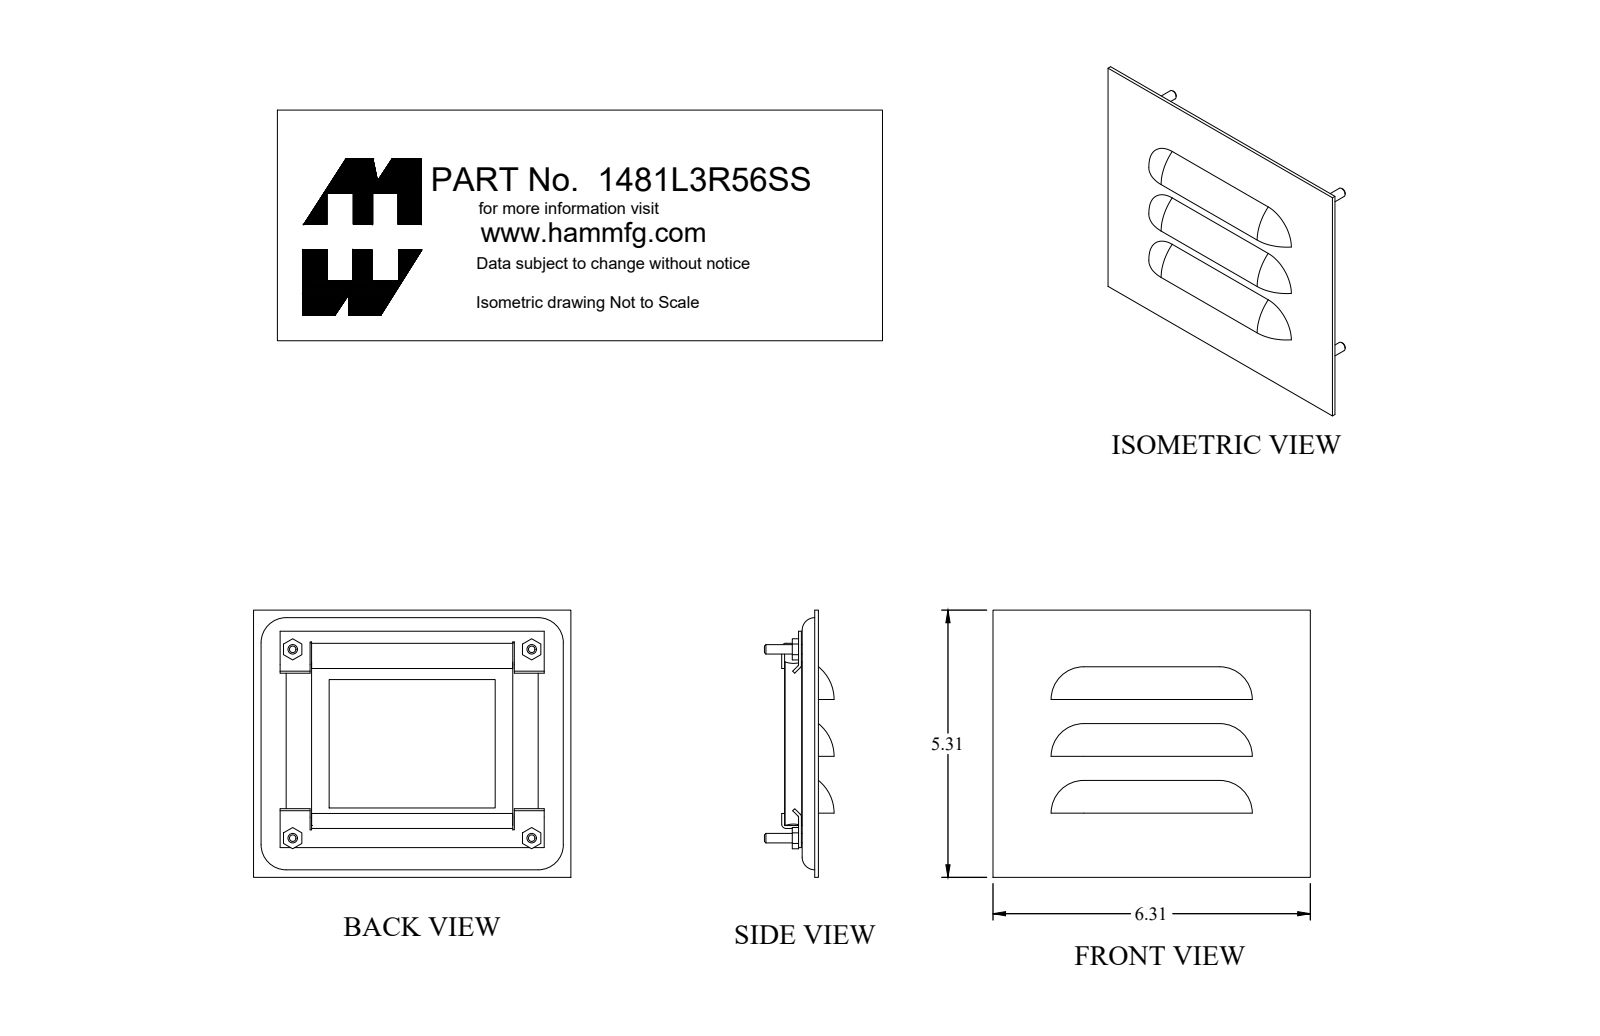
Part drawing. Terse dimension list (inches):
name: 1481L3R56SS_Default
written by: SolidWorks 2019 (CONFIG_CONTROL_DESIGN)
unit: in
bodies: 13 solids, 240 faces (138 planar, 70 cylindrical, 32 other)
size: 6.308 × 5.308 × 1.041
volume: 8.702 in³; area: 175 in²
holes: 4× ⌀0.156, 4× ⌀0.205
bosses: 4× ⌀0.25, 4× ⌀0.188
rounds: 6× R0.029, 6× R0.086, 4× R0.25, 4× R0.469, 4× R0.499, 3× R0.761, 3× R0.833
face distances: 0.072, 0.3, 0.25, 0.05, 0.073, 0.322, 0.372, 0.622, 0.55, 0.299
hole spacings: 3.75, 3.75, 4.75, 4.75, 6.051, 6.052, 6.052
